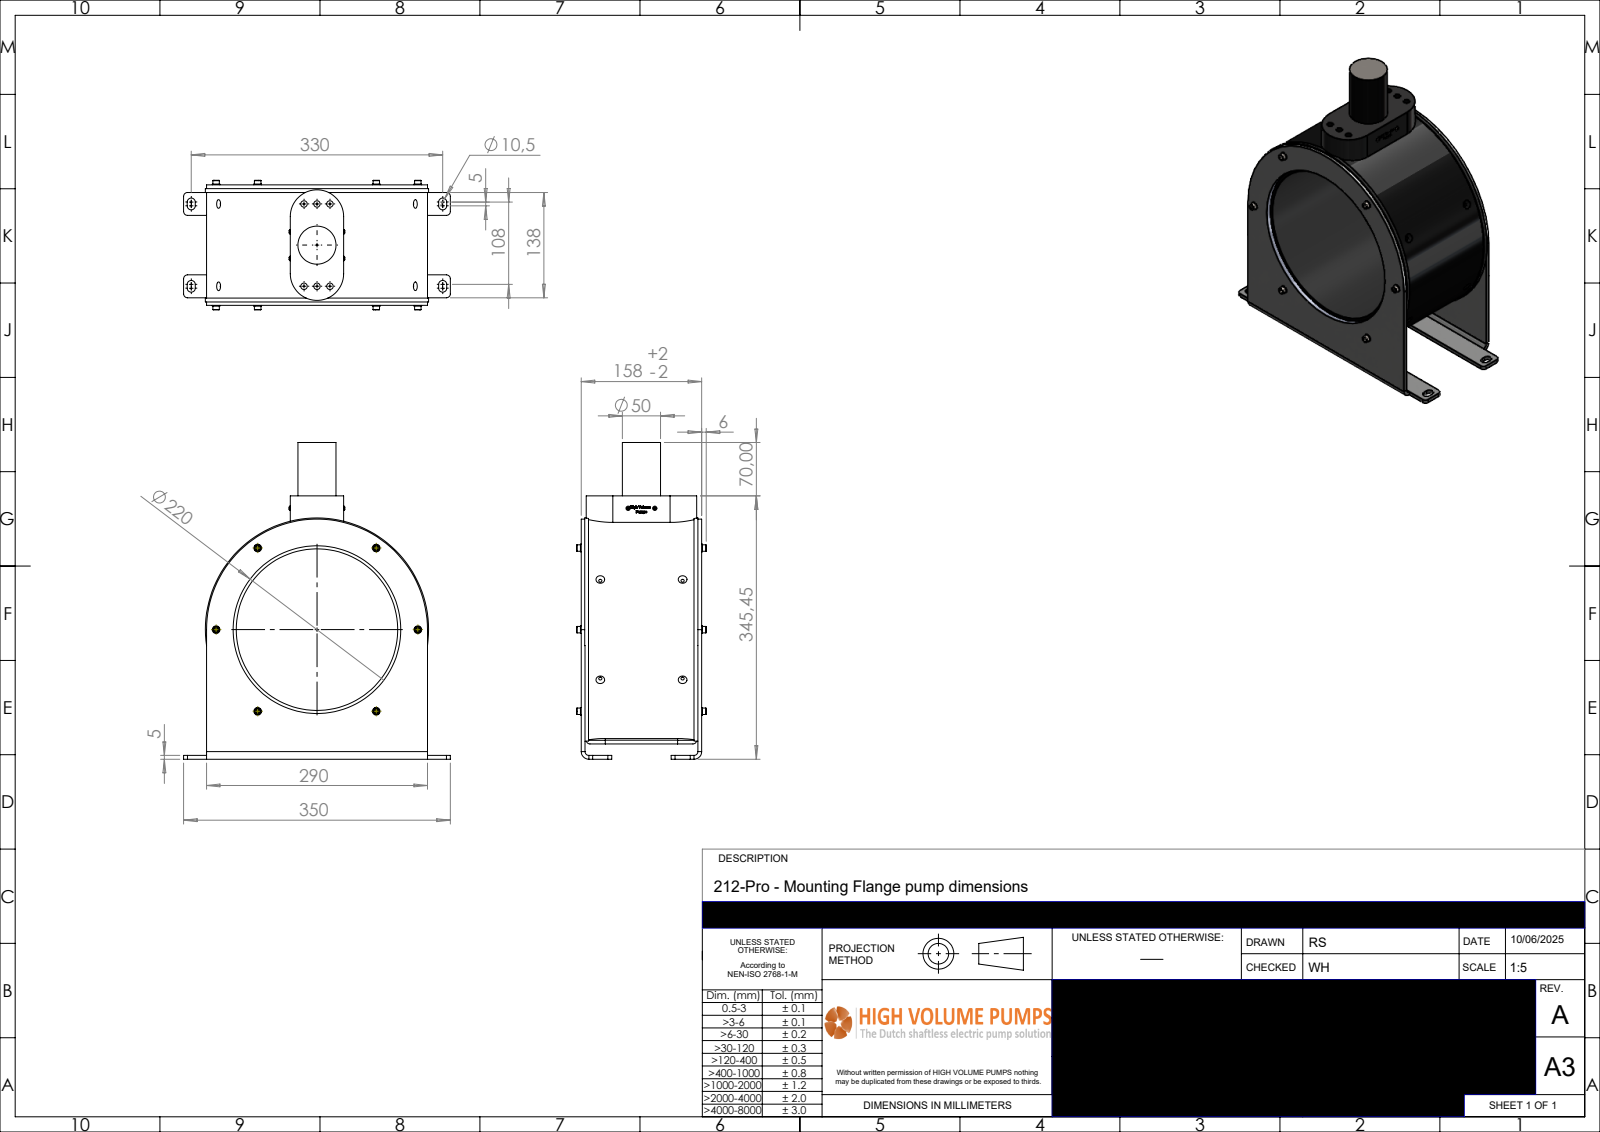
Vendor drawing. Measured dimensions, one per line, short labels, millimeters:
name: P-212-530-rev-A-MF
written by: SolidWorks 2024 (AUTOMOTIVE_DESIGN)
unit: mm
bodies: 1 solid, 893 faces (545 planar, 92 cylindrical, 256 other)
size: 415.45 × 350 × 170.06
volume: 5 565 000 mm³; area: 458 658 mm²
holes: 6× ⌀8.5, 4× ⌀4.2, 2× ⌀5.3, 1× ⌀212, 1× ⌀220
bosses: 6× ⌀10, 6× ⌀8.5, 2× ⌀9.64, 2× ⌀5.7, 2× ⌀5, 1× ⌀293, 1× ⌀290, 1× ⌀50
rounds: 12× R5, 8× R5.25, 2× R2, 2× R10, 2× R25, 2× R35, 1× R1
face distances: 5, 158.06, 153.06, 148.06, 345.45, 340.45, 151.56, 6.5, 1.5, 146.56
hole spacings: 108, 17, 109.33, 34, 113.23
